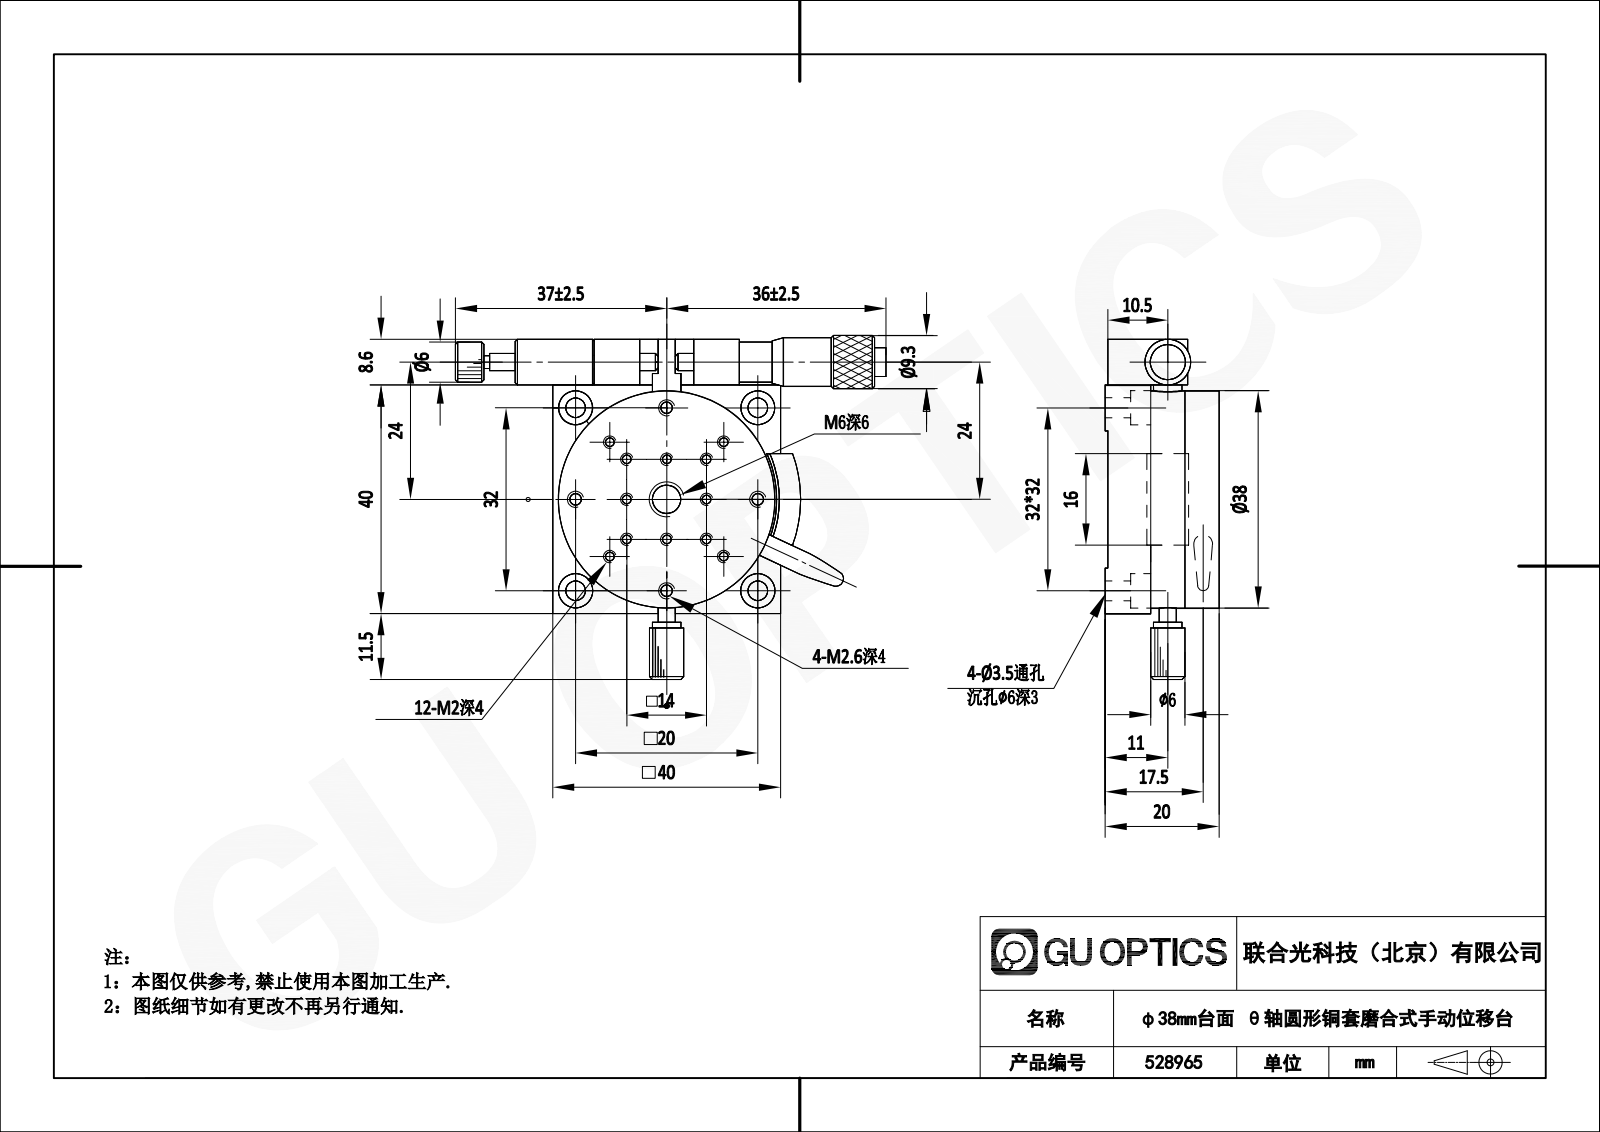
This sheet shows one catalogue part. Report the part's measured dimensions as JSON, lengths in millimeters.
{"part_name": "528965", "step_written_by": "SolidWorks 2020 (CONFIG_CONTROL_DESIGN)", "units": "millimeters", "bodies": {"solids": 0, "faces": 2433, "planar": 213, "cylindrical": 537, "other": 1683}, "overall_size": [77.31, 61.59, 20], "round_holes": [[1.57, 24], [2.5, 7], [2.8, 6], [3.5, 4], [4.2, 4], [6, 4], [1.57, 3], [2.01, 2], [2.01, 2], [2.11, 2], [2.11, 2], [4, 2]], "round_bosses_or_shafts": [[38, 1], [31, 1], [21, 1], [15.5, 1], [15, 1], [9.12, 1], [8.42, 1], [8, 1]], "partial_cylinders_radius": [[3, 1], [18.9, 1], [19.1, 1], [22, 1], [32, 1]], "face_to_face_distances": [6, 7.5, 3.5, 13.5, 4, 0.5, 12, 19.5, 10, 12.5], "hole_center_spacings": [7, 14.33, 7.16, 8.9, 9.55, 9.88, 9.9, 10.33]}
